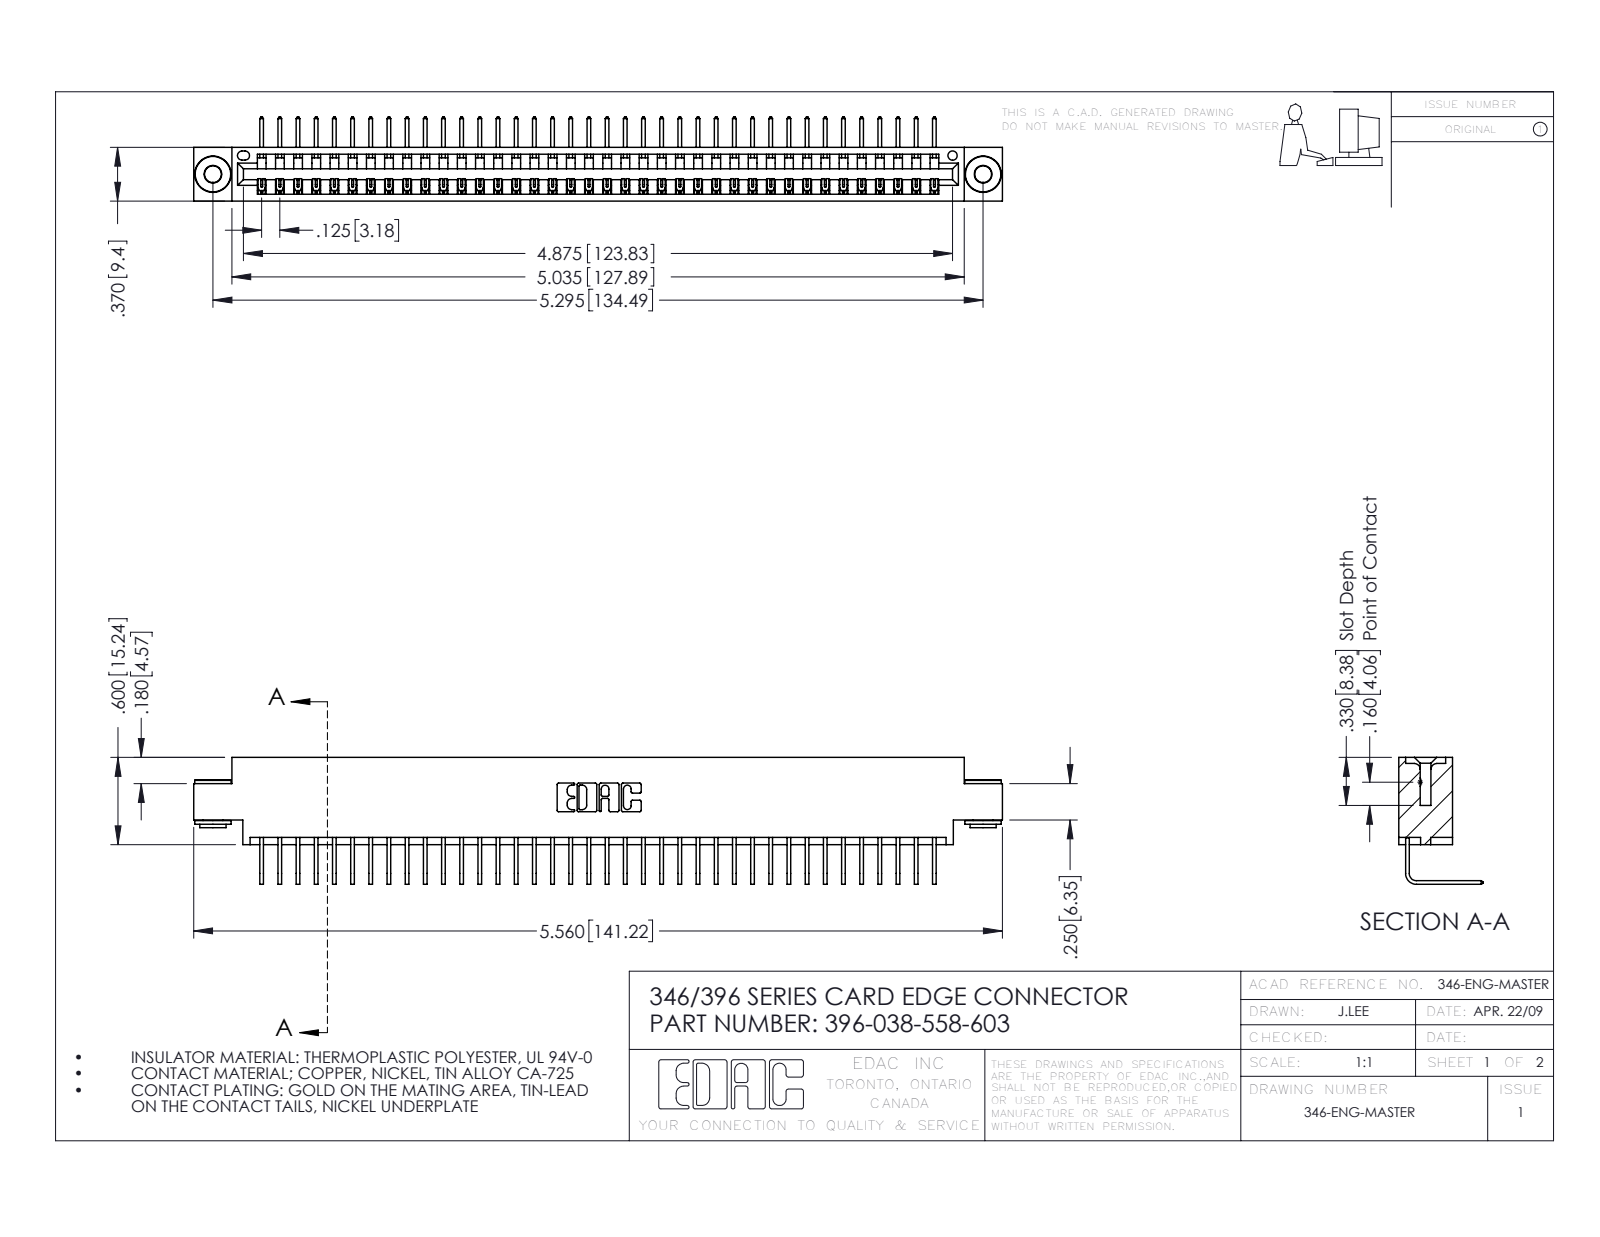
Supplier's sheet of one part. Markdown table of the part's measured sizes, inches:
| quantity | value |
| --- | --- |
| part name | 345-250-002_345-250-002-102; 345-292-001_558 Tail - 2; 396-038-558-603; 346 Part_0.170 Offset - 0.156 Dia-TH |
| STEP written by | SolidWorks 2016 (CONFIG_CONTROL_DESIGN) |
| units | inches |
| bodies | 41 solids, 2444 faces (1686 planar, 750 cylindrical, 8 other) |
| overall size | 5.56 × 0.873 × 0.58 |
| volume | 0.823 in³ |
| surface area | 27.81 in² |
| round holes (diameter × count) | 0.116 × 2, 0.156 × 2, 0.064 × 1 |
| round bosses / shafts (diameter × count) | 0.25 × 2, 0.18 × 2, 0.136 × 2 |
| partial cylindrical surfaces (radius × count) | 0.006 × 76, 0.01 × 22, 0.007 × 6, 0.031 × 6, 0.026 × 3, 0.031 × 2, 0.04 × 2, 0.014 × 1 |
| main face-to-face distances | 0.322, 0.048, 0.37, 0.25, 0.025, 0.298, 0.072, 0.148, 0.222, 0.1 |
| hole center spacings | 0.246, 5.086, 5.295 |
